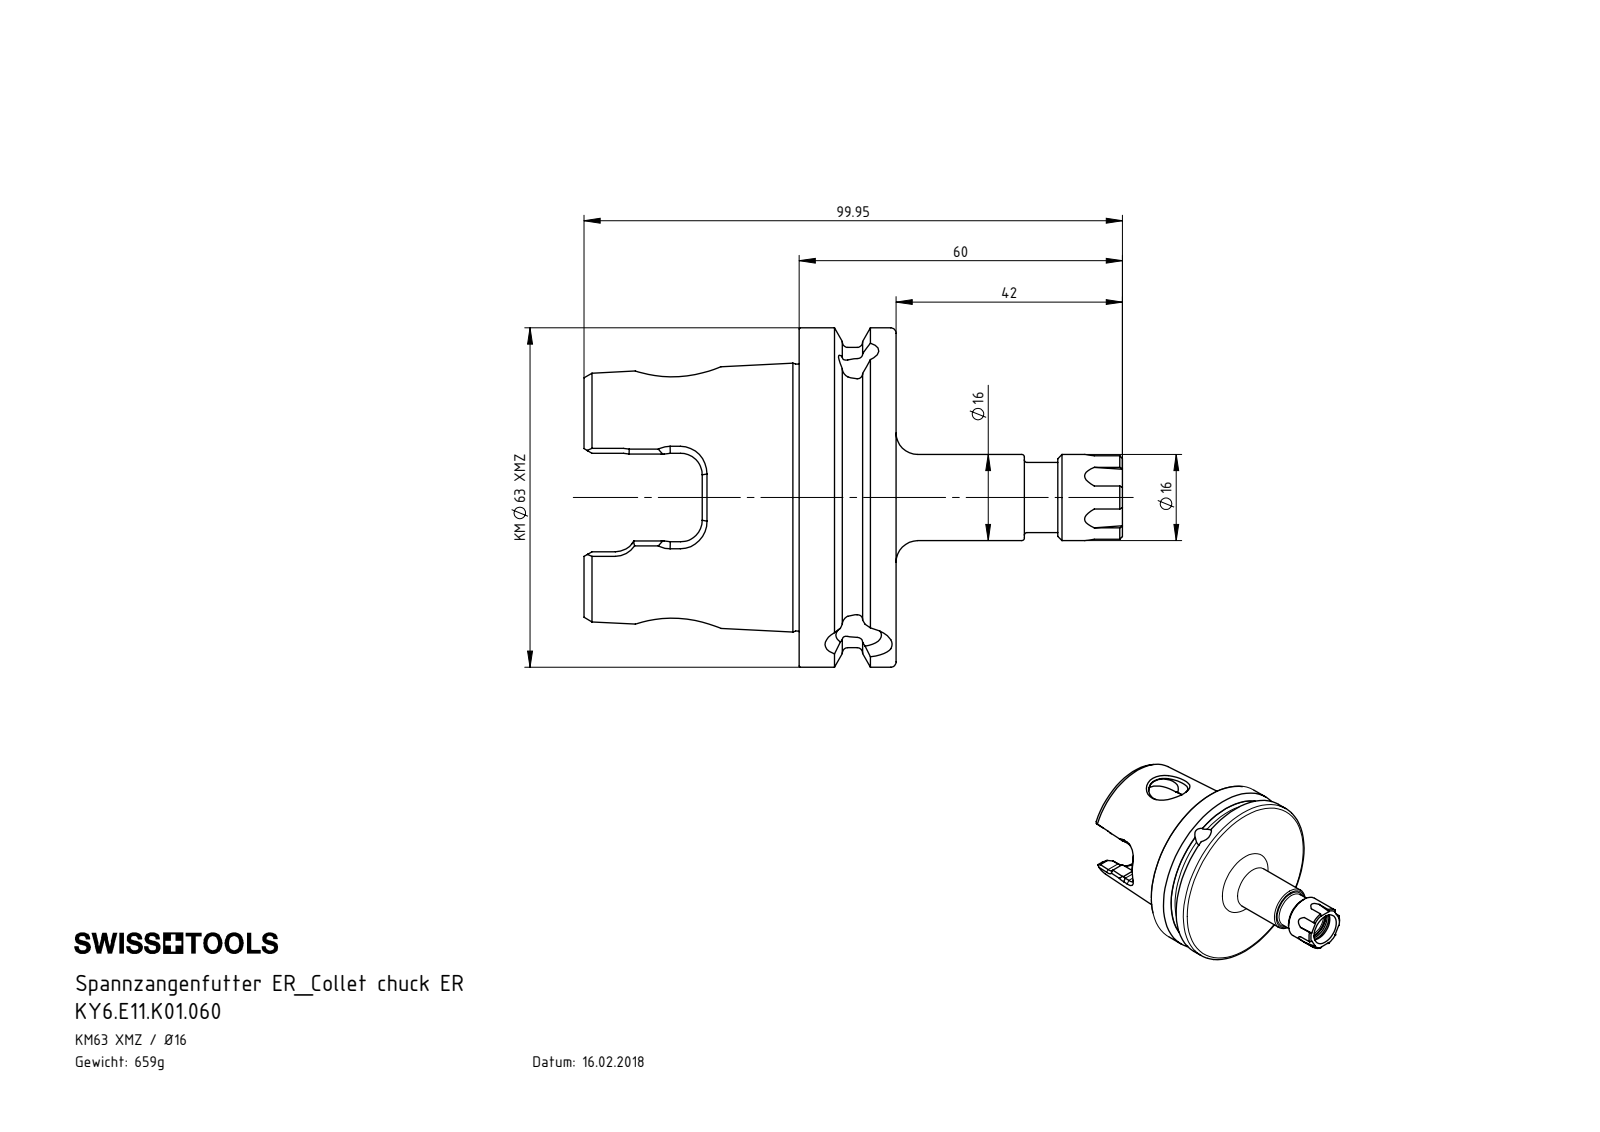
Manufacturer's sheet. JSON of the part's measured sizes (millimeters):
{"part_name": "KY6-E11.K01.060_B; KY6.E11.K01.060; E11-ER1.001.012", "step_written_by": "SolidWorks 2017 (CONFIG_CONTROL_DESIGN)", "units": "millimeters", "bodies": {"solids": 2, "faces": 273, "planar": 68, "cylindrical": 63, "other": 142}, "overall_size": [99.95, 62.95, 62.95], "volume_mm3": 83915, "surface_area_mm2": 23745, "round_holes": [[7.47, 2], [5, 1], [7.5, 1], [8.48, 1], [10, 1], [11.5, 1], [11.7, 1], [12.4, 1], [13.5, 1], [14.5, 1], [15.5, 1], [31.1, 1]], "round_bosses_or_shafts": [[62.95, 1], [55.7, 1], [16, 1], [13, 1]], "partial_cylinders_radius": [[4, 6], [7.04, 2]], "face_to_face_distances": [18, 1.1, 19.1, 6, 4.9, 24, 33.95, 38.85, 39.95, 57.95]}
